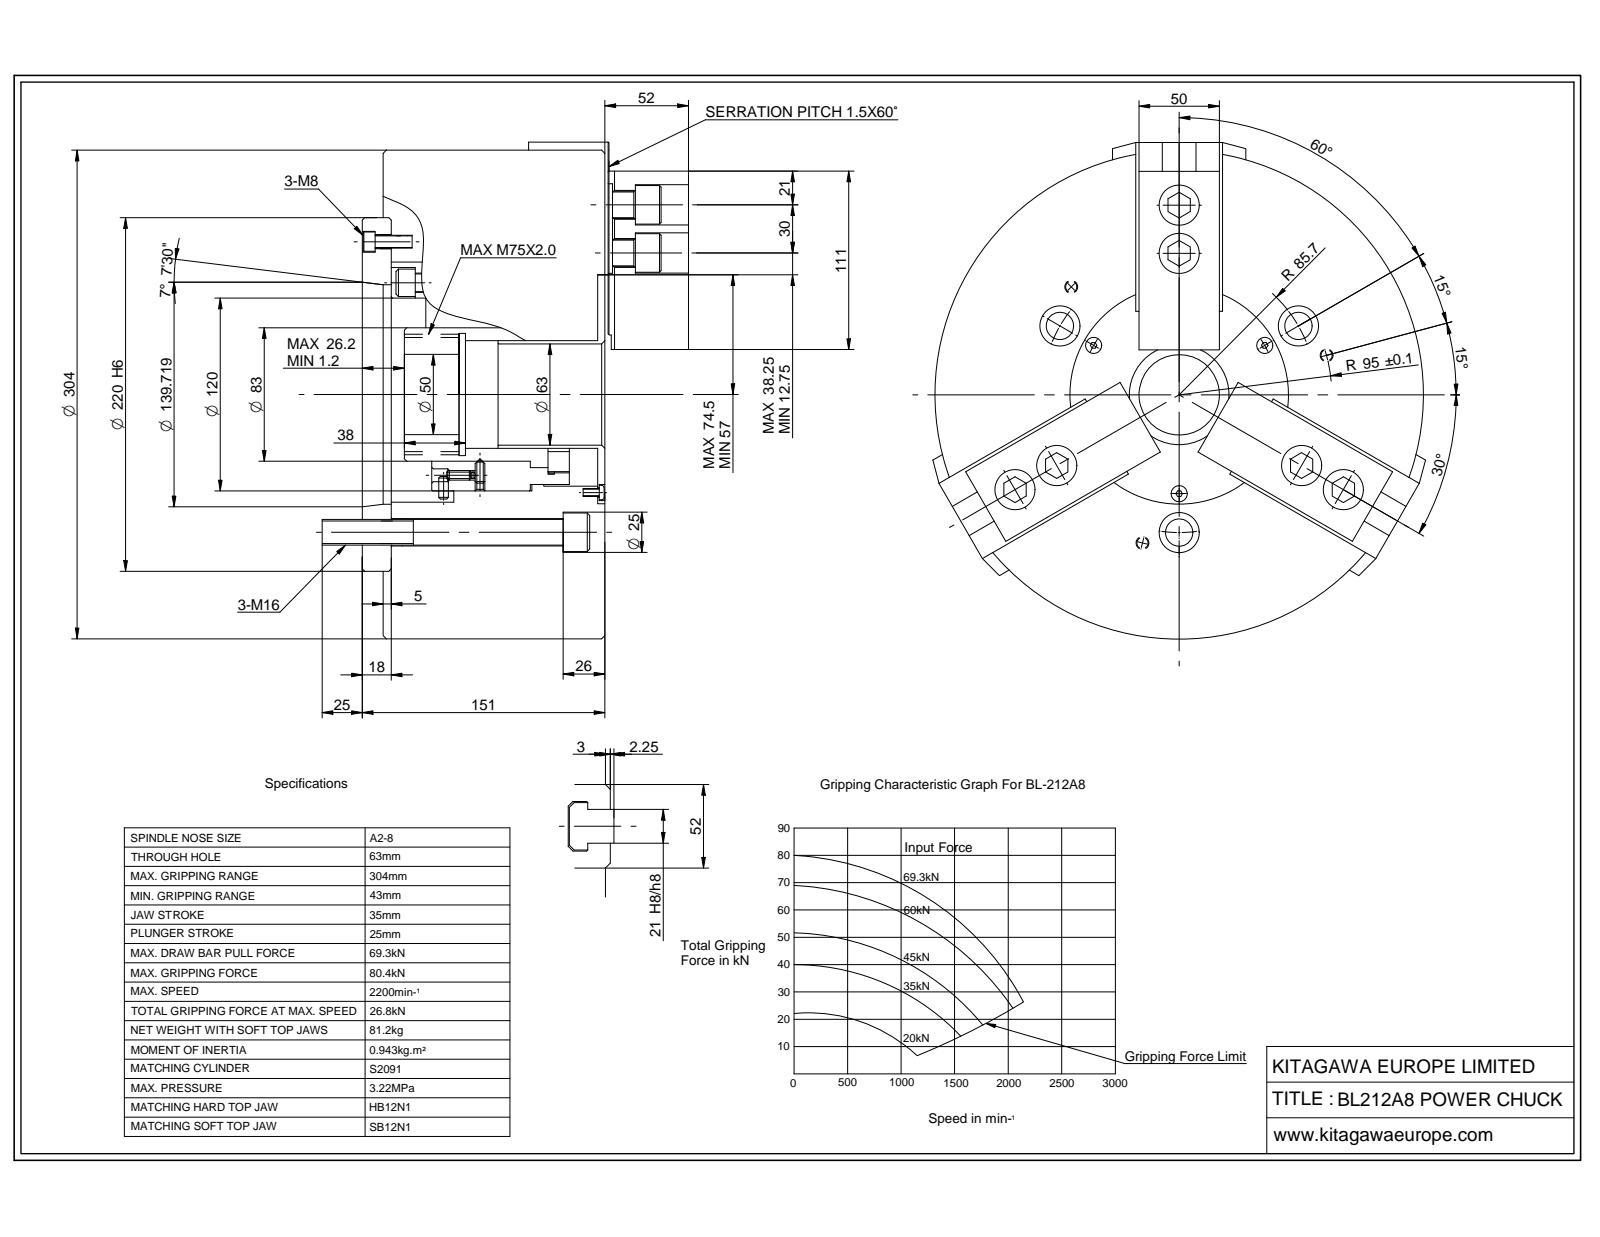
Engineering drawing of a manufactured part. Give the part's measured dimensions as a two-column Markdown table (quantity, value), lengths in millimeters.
| quantity | value |
| --- | --- |
| part name | BL212A8_mid stroke |
| STEP written by | ST-DEVELOPER v16.7 (AUTOMOTIVE_DESIGN) |
| units | millimeters |
| bodies | 45 solids, 4669 faces (3164 planar, 1188 cylindrical, 317 other) |
| overall size | 304 × 304 × 208.2 |
| volume | 9 751 000 mm³ |
| surface area | 1 138 000 mm² |
| round holes (diameter × count) | 17 × 21, 14 × 12, 3 × 9, 3.8 × 9, 10 × 9, 25 × 9, 5.2 × 8, 4.2 × 6, 6.8 × 6, 8.5 × 6, 5.5 × 5, 9.5 × 5 |
| round bosses / shafts (diameter × count) | 24 × 9, 15.68 × 9, 16 × 6, 9.73 × 6, 23.5 × 3, 9.5 × 3, 6 × 3, 4.83 × 3 |
| partial cylindrical surfaces (radius × count) | 0.1 × 393, 0.8 × 27, 1.2 × 18, 0.6 × 12, 7.5 × 12, 13 × 9, 1.4 × 6, 4 × 6 |
| main face-to-face distances | 133, 5, 18, 138, 51, 1, 90, 108, 6, 38 |
| hole center spacings | 26.65, 43.36, 65.7, 66.2, 69, 76.48, 85.7, 85.71 |
